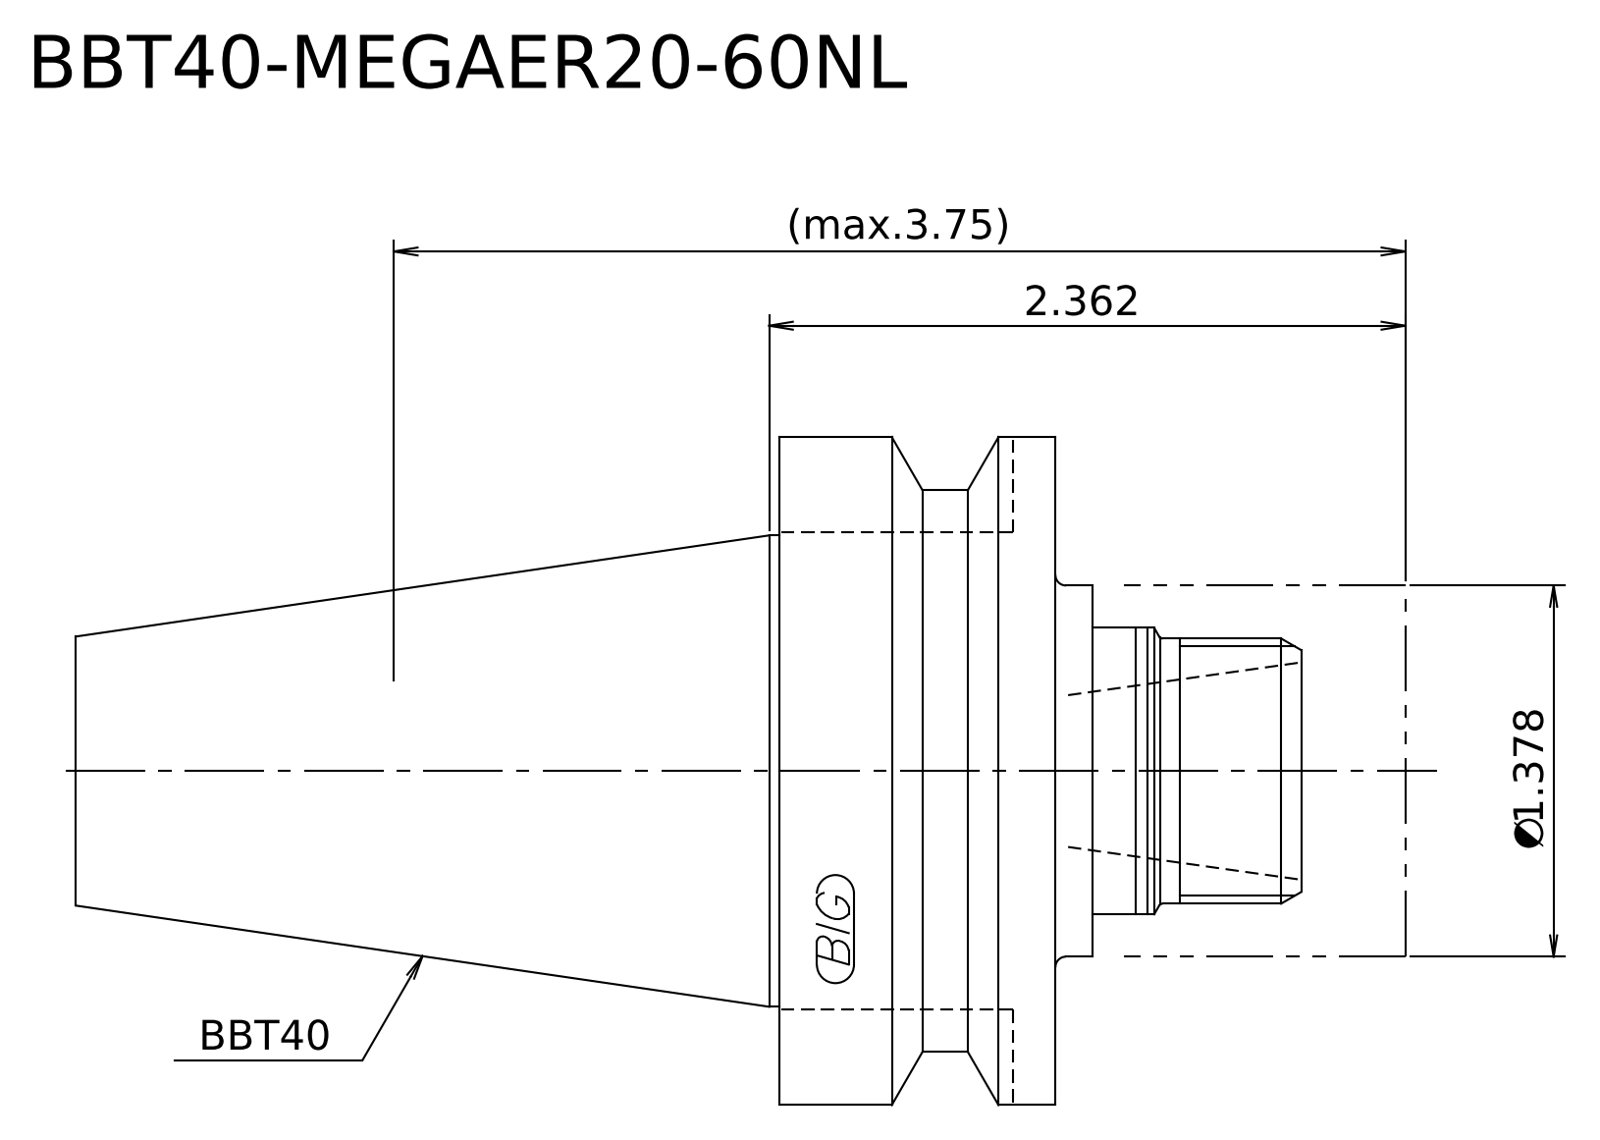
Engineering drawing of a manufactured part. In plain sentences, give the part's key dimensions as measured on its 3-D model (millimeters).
Its 3-D file was written by "Kubotek KeyCreator 2011 V10.0.2 (22737) (automotive_design)". It is 2 solids with 21 faces: 7 planar, 8 cylindrical and 6 other. Overall it measures 125.4 by 63 by 63 millimeters. Its volume is 179 155 cubic millimeters and its surface area 25 193 square millimeters. Round bosses or shafts: 1 of diameter 63, 1 of diameter 53, 1 of diameter 44.45, 1 of diameter 35, 1 of diameter 27, 1 of diameter 25. The main face-to-face distances are 26, 6.5, 32.5, 26.5, 33, 59, 29.5, 125.4, 98.9, 92.4.
